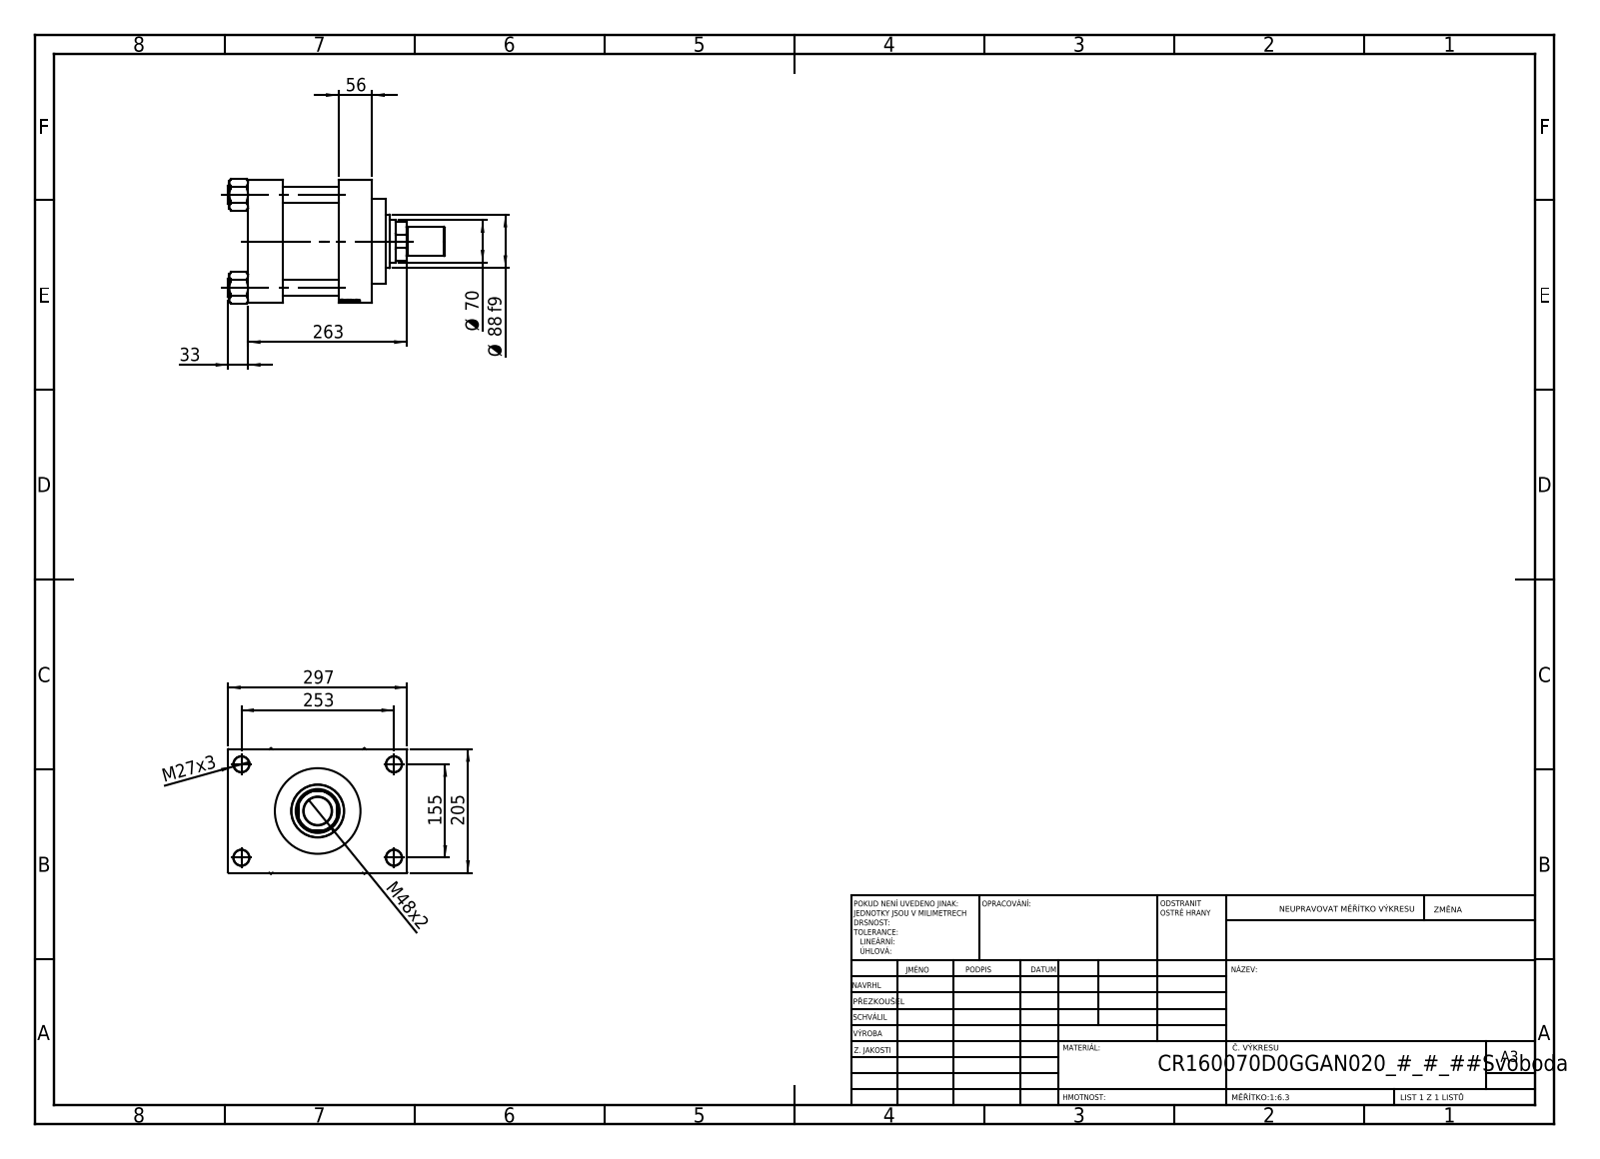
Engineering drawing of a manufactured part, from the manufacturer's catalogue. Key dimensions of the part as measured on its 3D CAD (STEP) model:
Part name (STEP PRODUCT): V215CR_D_Body; NUT_M5_D; V215CR_VCP_D; V215_VC_A (+2 more)
STEP written by: SolidWorks 2019 (CONFIG_CONTROL_DESIGN)
Units: millimetres
Bodies: 12 solids, 1163 faces (548 planar, 91 cylindrical, 524 other)
Overall size (bounding box): 359 × 297 × 208.14
Volume: 8 009 000 mm³ · Surface area: 738 229 mm²
Round holes (diameter × count): ⌀26 ×4, ⌀27 ×4, ⌀7 ×2, ⌀33.24 ×2, ⌀45 ×2, ⌀46.5 ×1, ⌀70 ×1, ⌀73 ×1, ⌀120 ×1, ⌀142 ×1, ⌀160 ×1
Round bosses / shafts (diameter × count): ⌀30 ×4, ⌀166 ×1, ⌀88 ×1, ⌀48 ×1, ⌀46 ×1
Partial cylindrical surfaces — rounded edges, fillets, slot ends (radius × count): R34 ×1
Main face-to-face distances: 58, 150, 92, 206, 148, 56, 205, 46, 251, 72
Hole centre spacings: 49.05, 109.53, 148.35, 154.9, 162.53, 203.95, 256.13, 155
